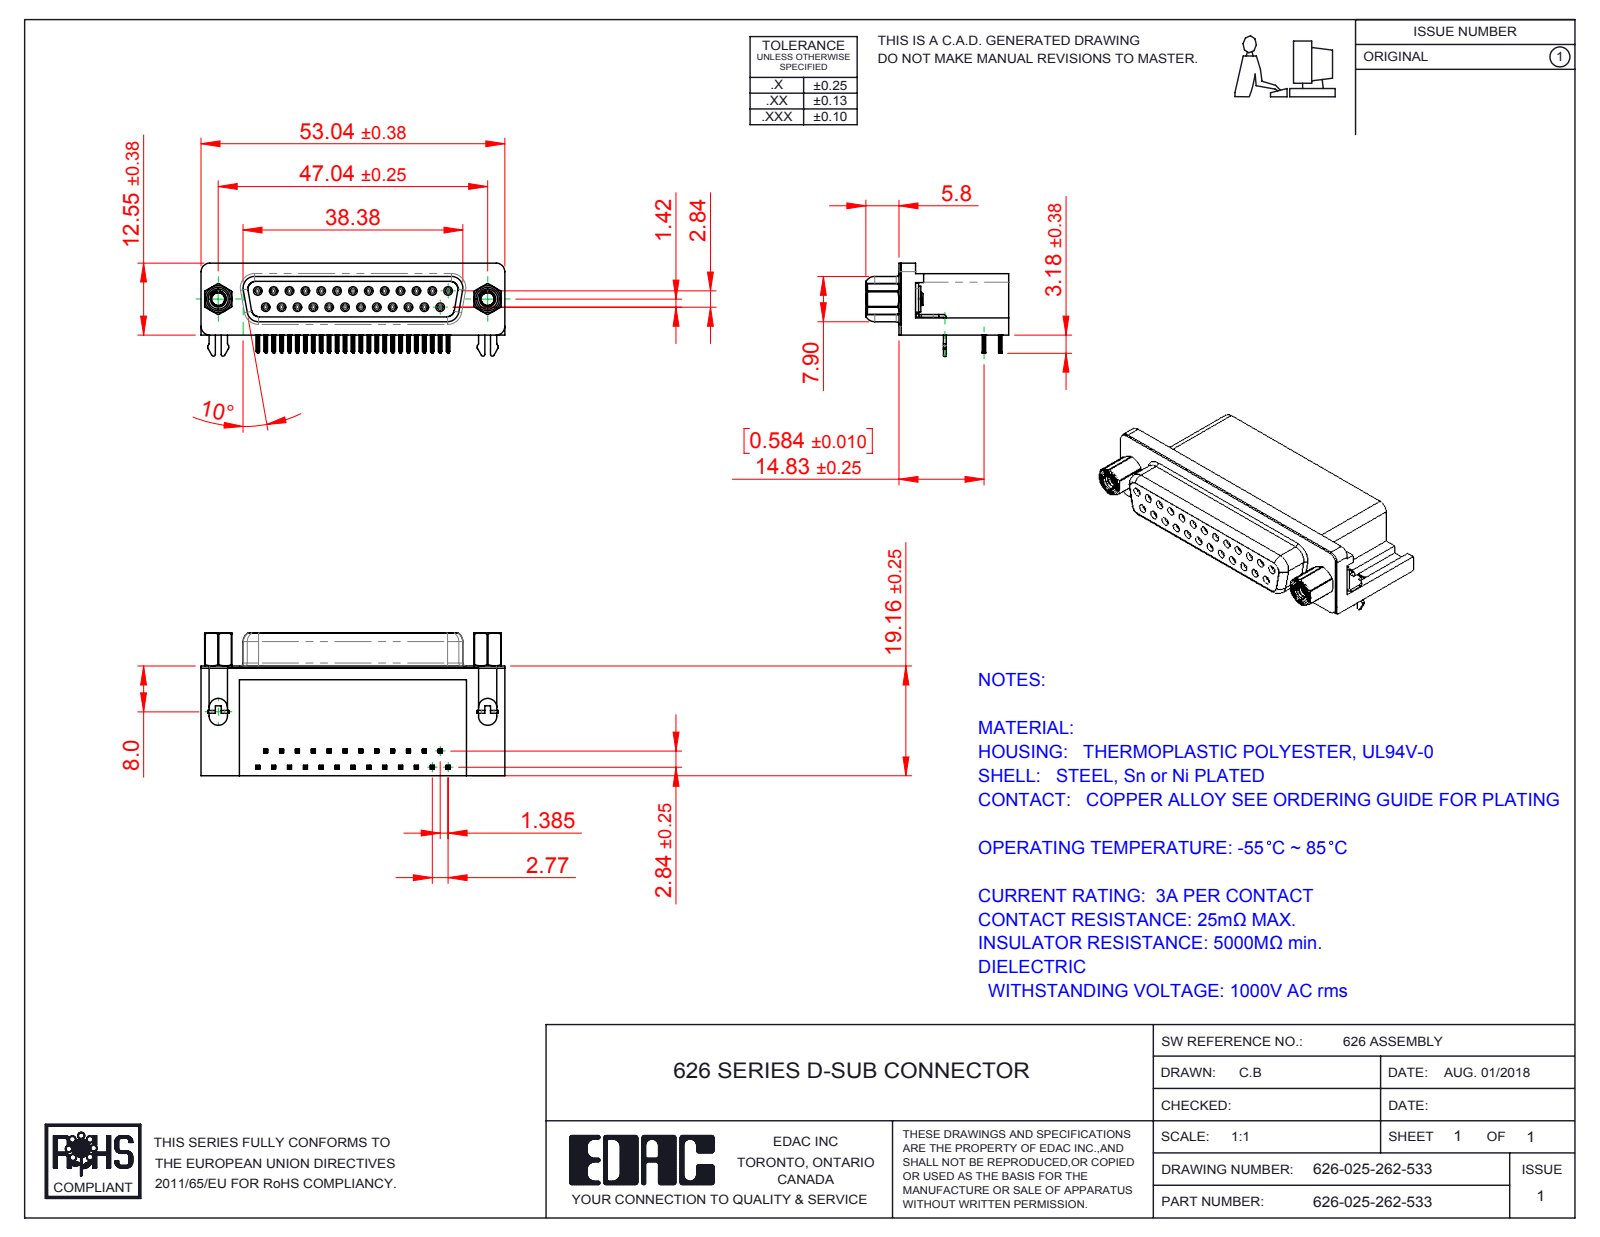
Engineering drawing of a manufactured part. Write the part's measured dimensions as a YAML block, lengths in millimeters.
part_name: "626 Shell_25 Socket; 626 Contact Top; 626 Round Threaded Standoff; 626 Contact Bottom (+4 more)"
step_written_by: "SolidWorks 2016 (CONFIG_CONTROL_DESIGN)"
units: millimeters
bodies: {solids: 33, faces: 4010, planar: 1768, cylindrical: 1008, other: 1234}
overall_size: [53.04, 24.96, 16.25]
volume: 10972
surface_area: 12053
round_holes:
  - {diameter: 0.8, count: 25}
  - {diameter: 0.9, count: 25}
  - {diameter: 2.29, count: 2}
  - {diameter: 2.3, count: 2}
  - {diameter: 3.1, count: 2}
  - {diameter: 4, count: 2}
  - {diameter: 4.8, count: 2}
  - {diameter: 5, count: 2}
round_bosses_or_shafts:
  - {diameter: 1.2, count: 25}
  - {diameter: 4.9, count: 2}
  - {diameter: 4.7, count: 2}
  - {diameter: 4.5, count: 2}
  - {diameter: 3.85, count: 2}
  - {diameter: 2.79, count: 2}
partial_cylinders:
  - {radius: 0.1, count: 200}
  - {radius: 0.15, count: 100}
  - {radius: 0.35, count: 50}
  - {radius: 0.34, count: 25}
  - {radius: 1, count: 18}
  - {radius: 0.28, count: 12}
  - {radius: 0.5, count: 10}
  - {radius: 1.35, count: 8}
face_to_face_distances: [0.4, 10.35, 18.76, 6.2, 2.73, 2.84, 9.38, 3.18, 0.35, 0.85]
hole_center_spacings: [3.16, 2.77, 5.54, 8.31, 11.08, 5.03, 5.04, 7.48]
